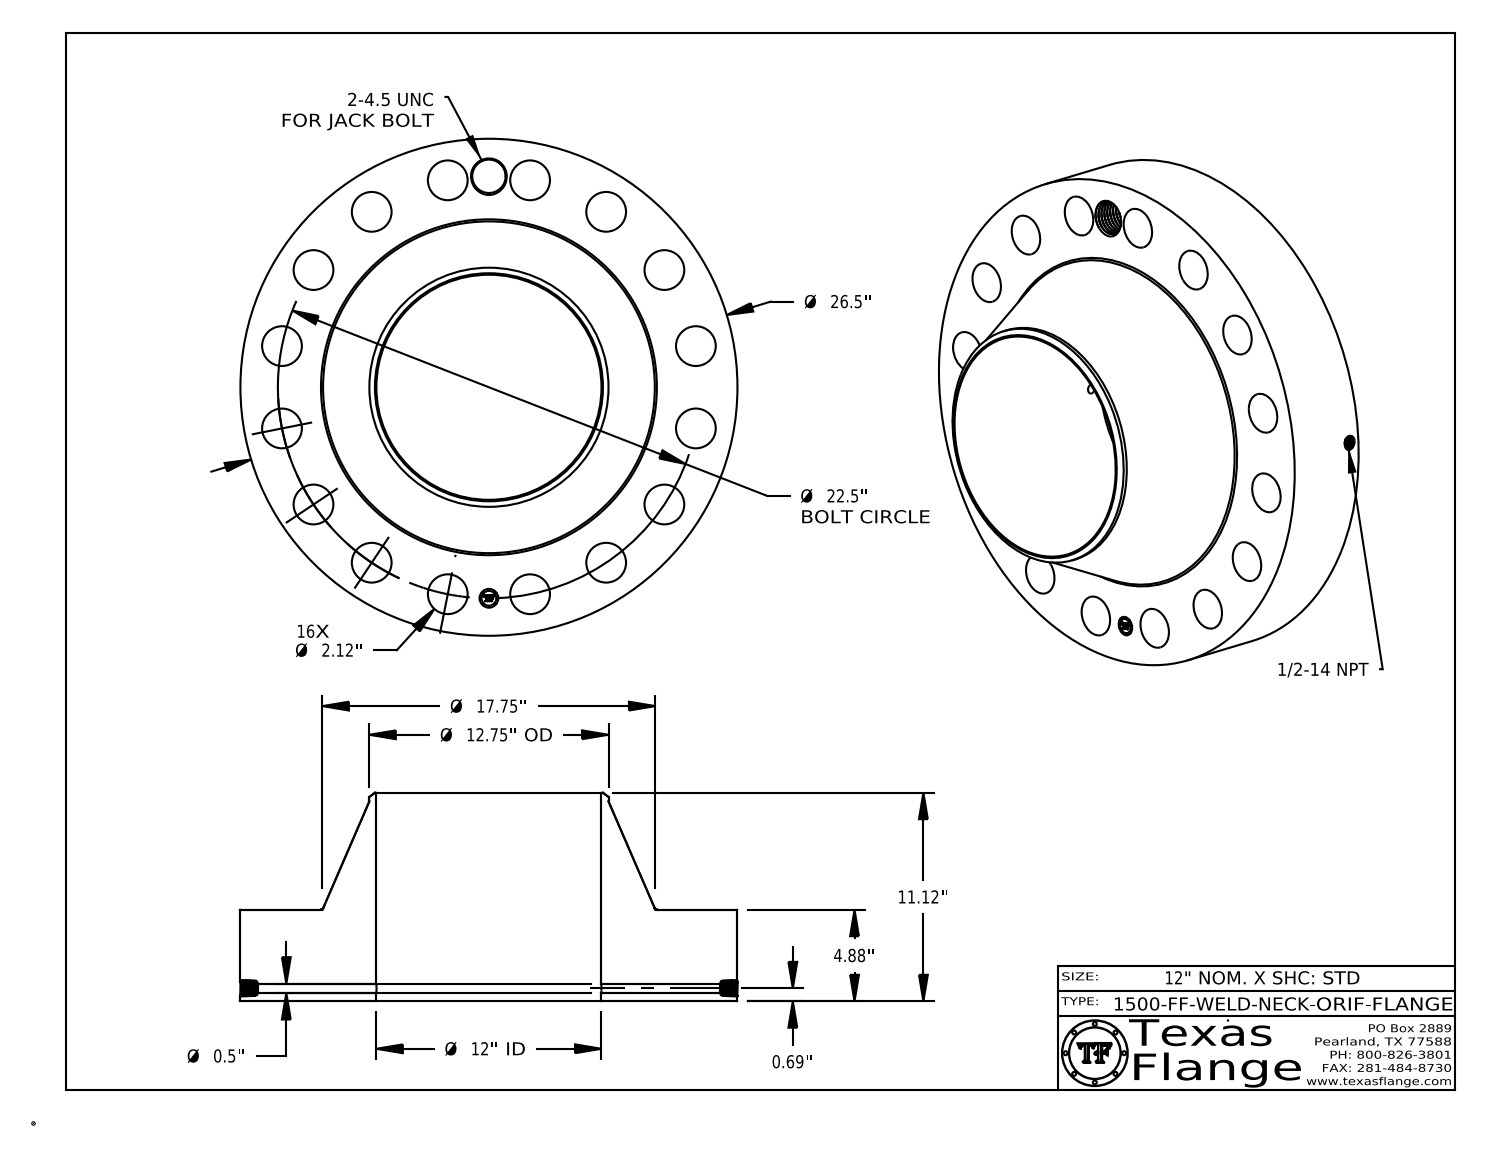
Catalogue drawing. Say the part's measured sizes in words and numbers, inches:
The part is named "1500-FF-WELD-NECK". Its 3-D file was written by "CATIA V5 STEP AP214 (AUTOMOTIVE_DESIGN)". It is 1 solid with 824 faces: 368 planar, 122 cylindrical and 334 other. Overall it measures 26.5 by 26.5 by 11.12 inches. Its volume is 2 264 cubic inches and its surface area 2 364 square inches. Round holes: 16 of diameter 2.12, 1 of diameter 0.5, 1 of diameter 0.672, 1 of diameter 1, 1 of diameter 1.781, 1 of diameter 12. Round bosses or shafts: 8 of diameter 0.061, 1 of diameter 26.5, 1 of diameter 12.75, 1 of diameter 0.788. The main face-to-face distances are 4.88, 11.12, 6.24, 4.865, 0.015, 6.255, 0.298, 0.293, 0.054, 0.248. The hole center spacings are 11.25, 8.61, 15.91, 20.787, 12.5, 18.708, 22.068, 4.389.
